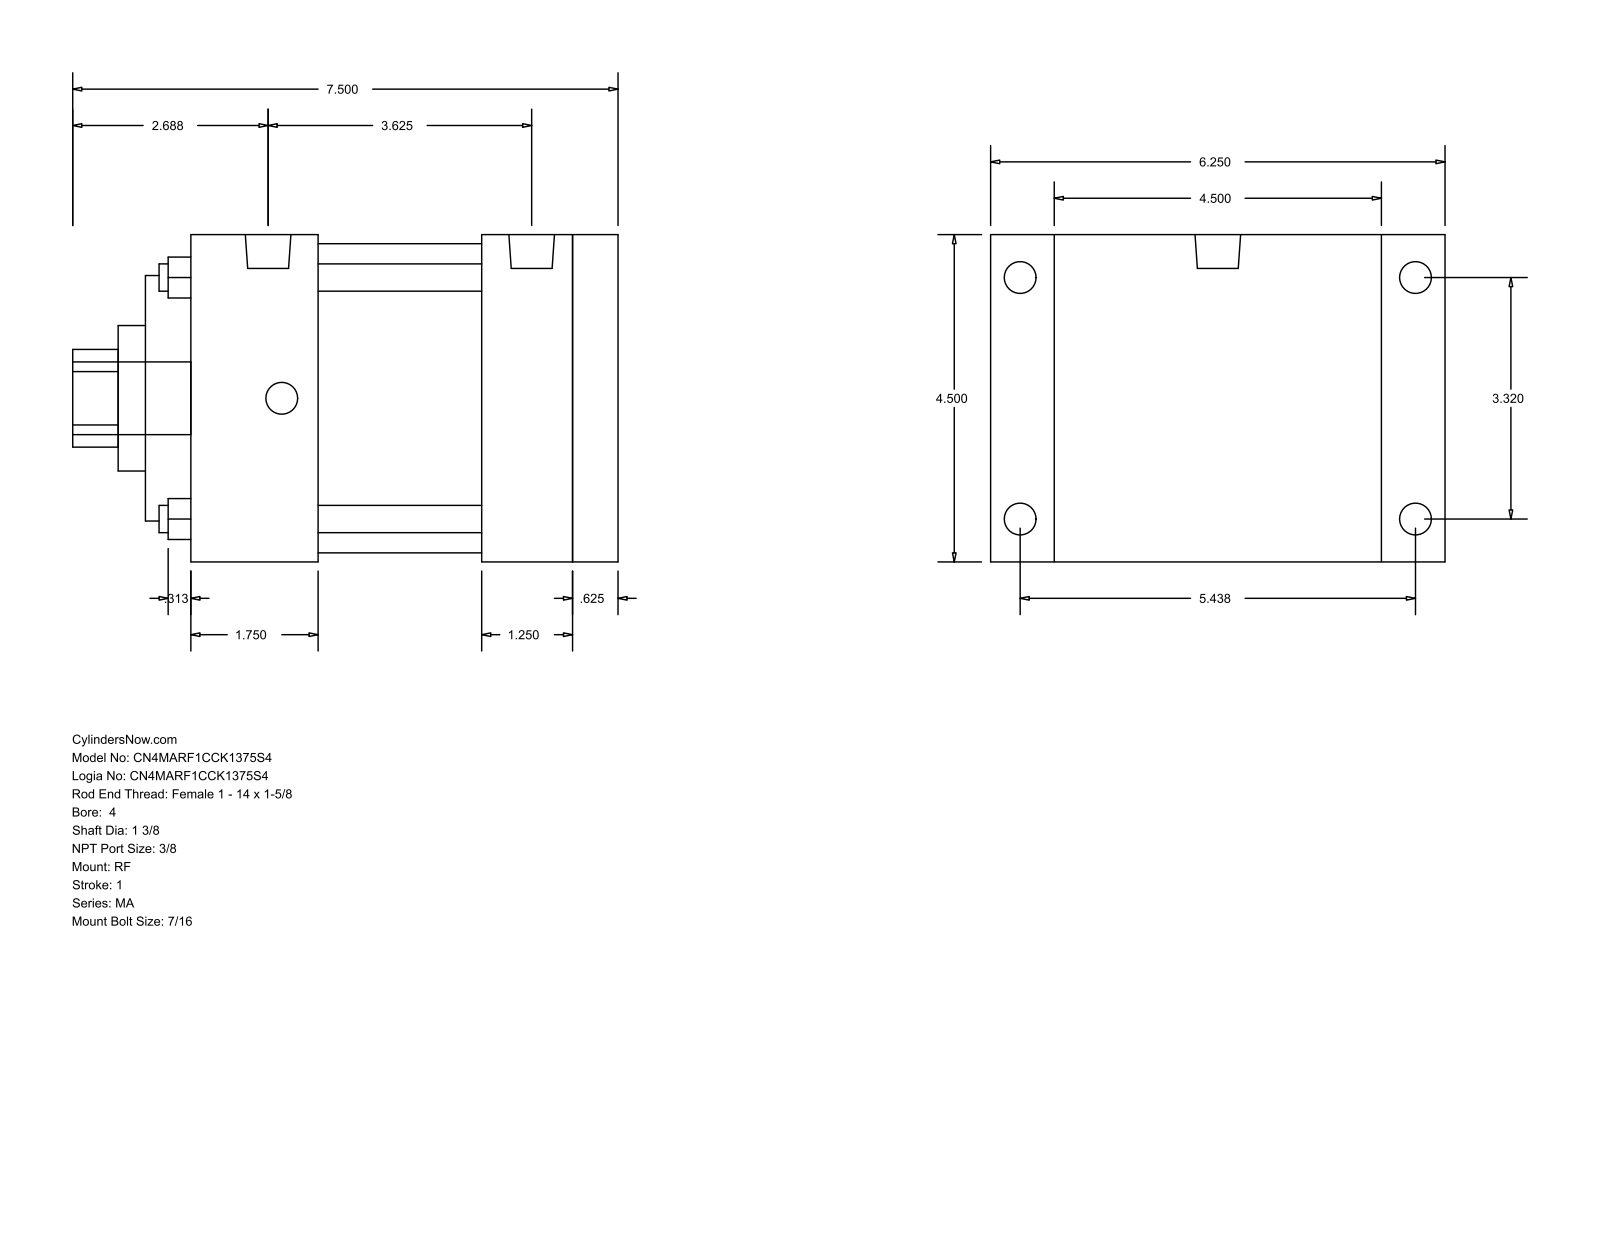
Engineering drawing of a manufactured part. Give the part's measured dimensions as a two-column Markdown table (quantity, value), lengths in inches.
| quantity | value |
| --- | --- |
| part name | MA_RF__0400_1.375 |
| STEP written by | GSSL Pune (CONFIG_CONTROL_DESIGN) |
| units | inches |
| bodies | 0 solids, 94 faces (65 planar, 29 cylindrical, 0 other) |
| overall size | 7.5 × 6.25 × 4.5 |
| round holes (diameter × count) | 0.375 × 4, 1.375 × 1, 2 × 1, 3.375 × 1, 4.25 × 1 |
| round bosses / shafts (diameter × count) | 0.437 × 8, 0.627 × 2, 1 × 1 |
| partial cylindrical surfaces (radius × count) | 0.672 × 1 |
| main face-to-face distances | 4.5, 5.875, 0.625, 5.25, 0.625, 5.875, 6.5, 0.875, 5.375, 4.625 |
| hole center spacings | 2.347, 3.32, 4.695 |
